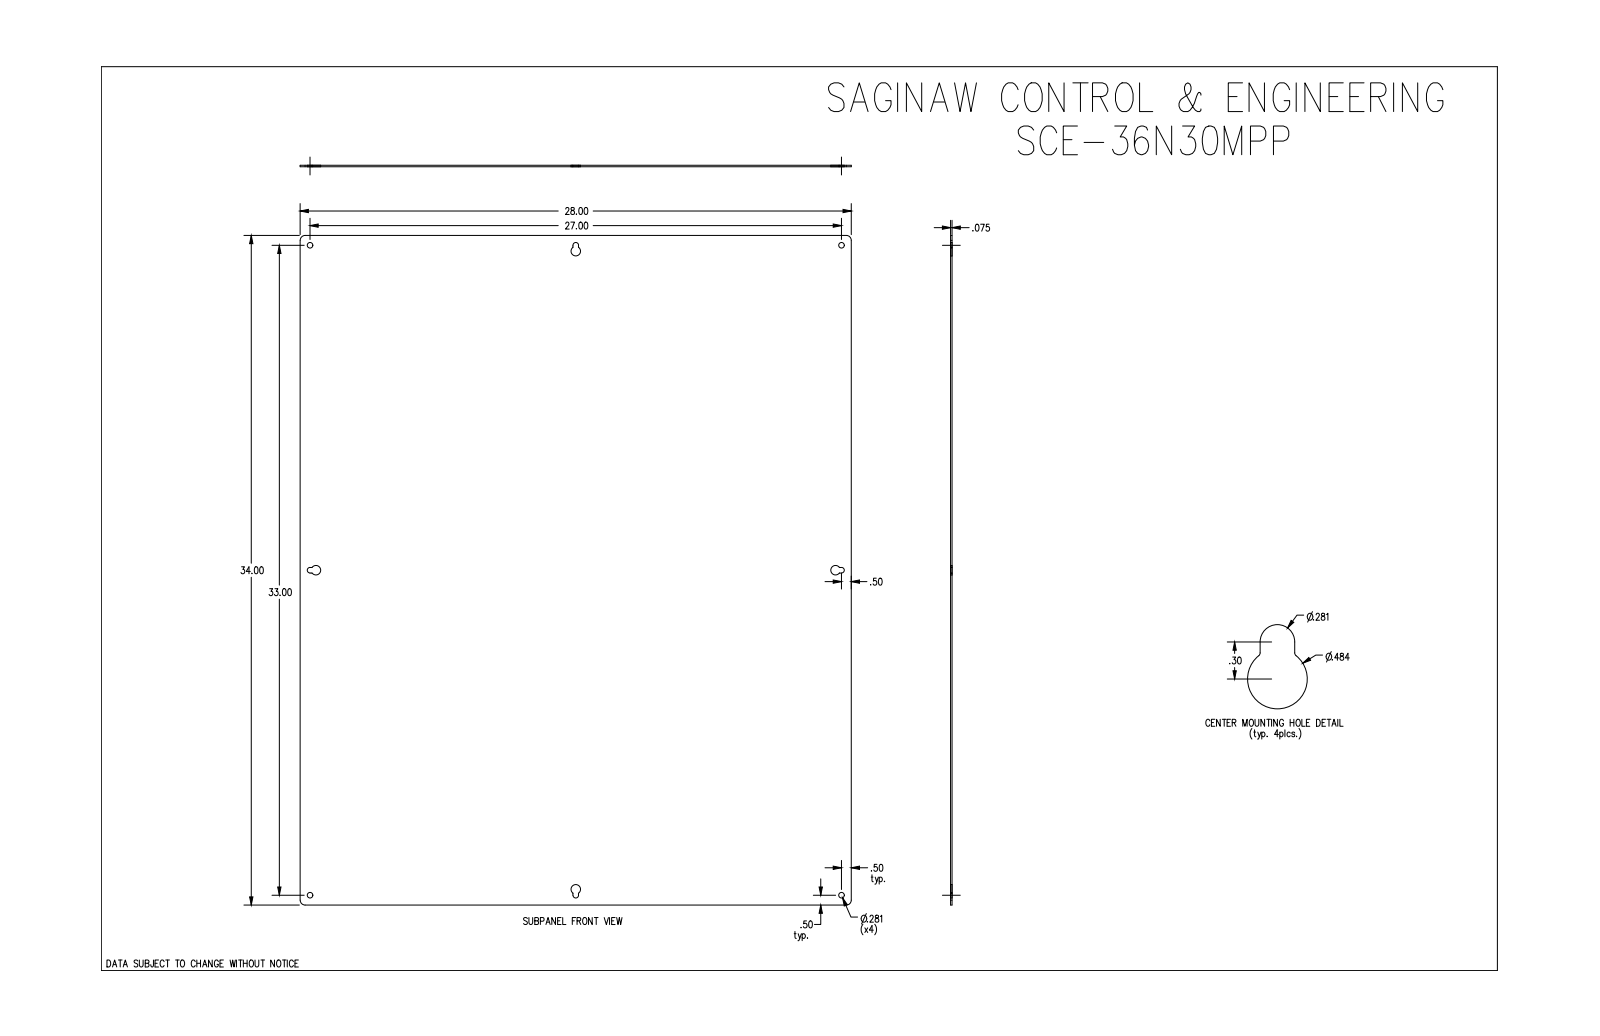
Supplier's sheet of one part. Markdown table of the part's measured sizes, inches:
| quantity | value |
| --- | --- |
| part name | SCE-36N30MPP |
| STEP written by | SolidWorks 2019 (CONFIG_CONTROL_DESIGN) |
| units | inches |
| bodies | 1 solid, 38 faces (14 planar, 24 cylindrical, 0 other) |
| overall size | 34 × 28 × 0.075 |
| volume | 71.31 in³ |
| surface area | 1 912 in² |
| round holes (diameter × count) | 0.281 × 4 |
| partial cylindrical surfaces (radius × count) | 0.03 × 8, 0.141 × 4, 0.242 × 4, 0.25 × 4 |
| main face-to-face distances | 0.075, 28, 34, 16.859, 17.141, 0.281, 13.859, 14.141 |
| hole center spacings | 27, 33, 42.638 |
